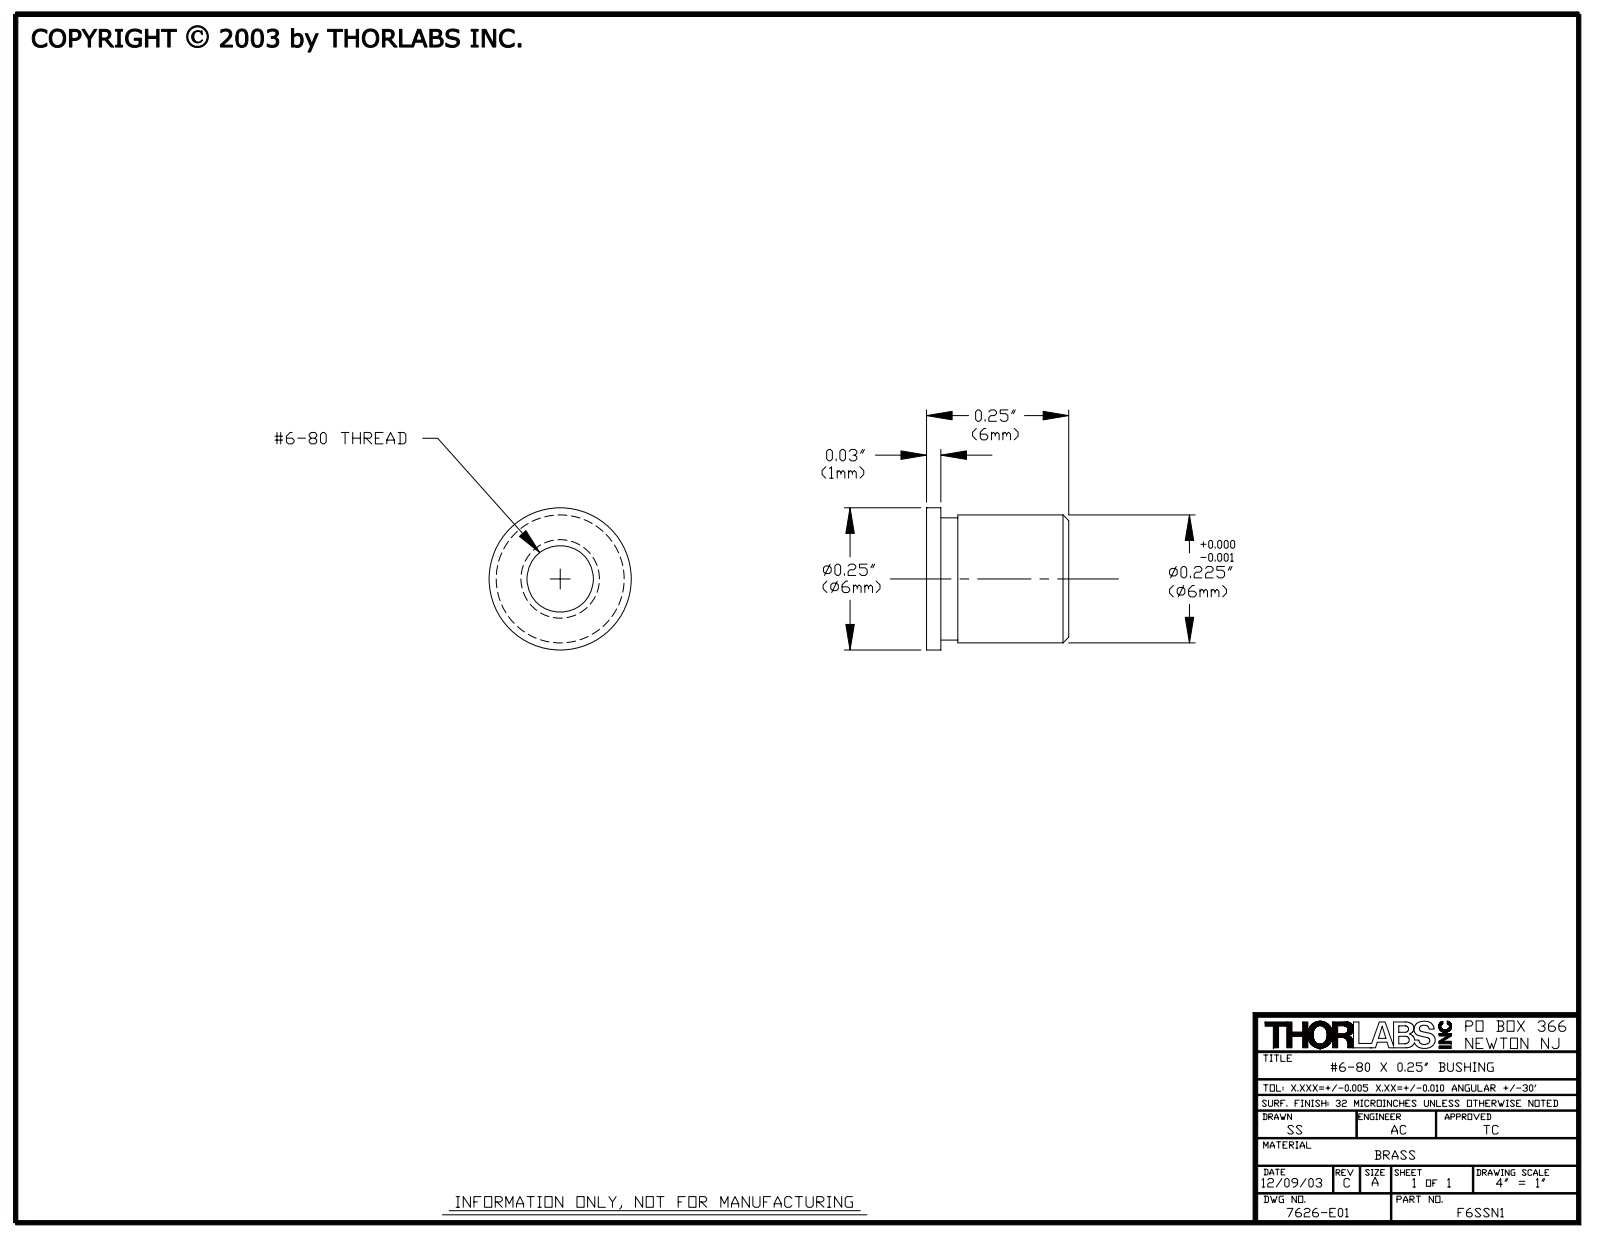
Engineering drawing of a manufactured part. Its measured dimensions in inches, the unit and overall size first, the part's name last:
Units: inches
Overall size (bounding box): 0.25 × 0.25 × 0.25
Round holes (diameter × count): ⌀0.104 ×1
Round bosses / shafts (diameter × count): ⌀0.25 ×1, ⌀0.225 ×1
Main face-to-face distances: 0.25, 0.225, 0.025
Volume: 0.008 in³ · Surface area: 0.333 in²
Bodies: 1 solid, 15 faces (3 planar, 6 cylindrical, 6 other)
Part name (STEP PRODUCT): 7626-E0W
STEP written by: SolidWorks 2007 (AUTOMOTIVE_DESIGN)
